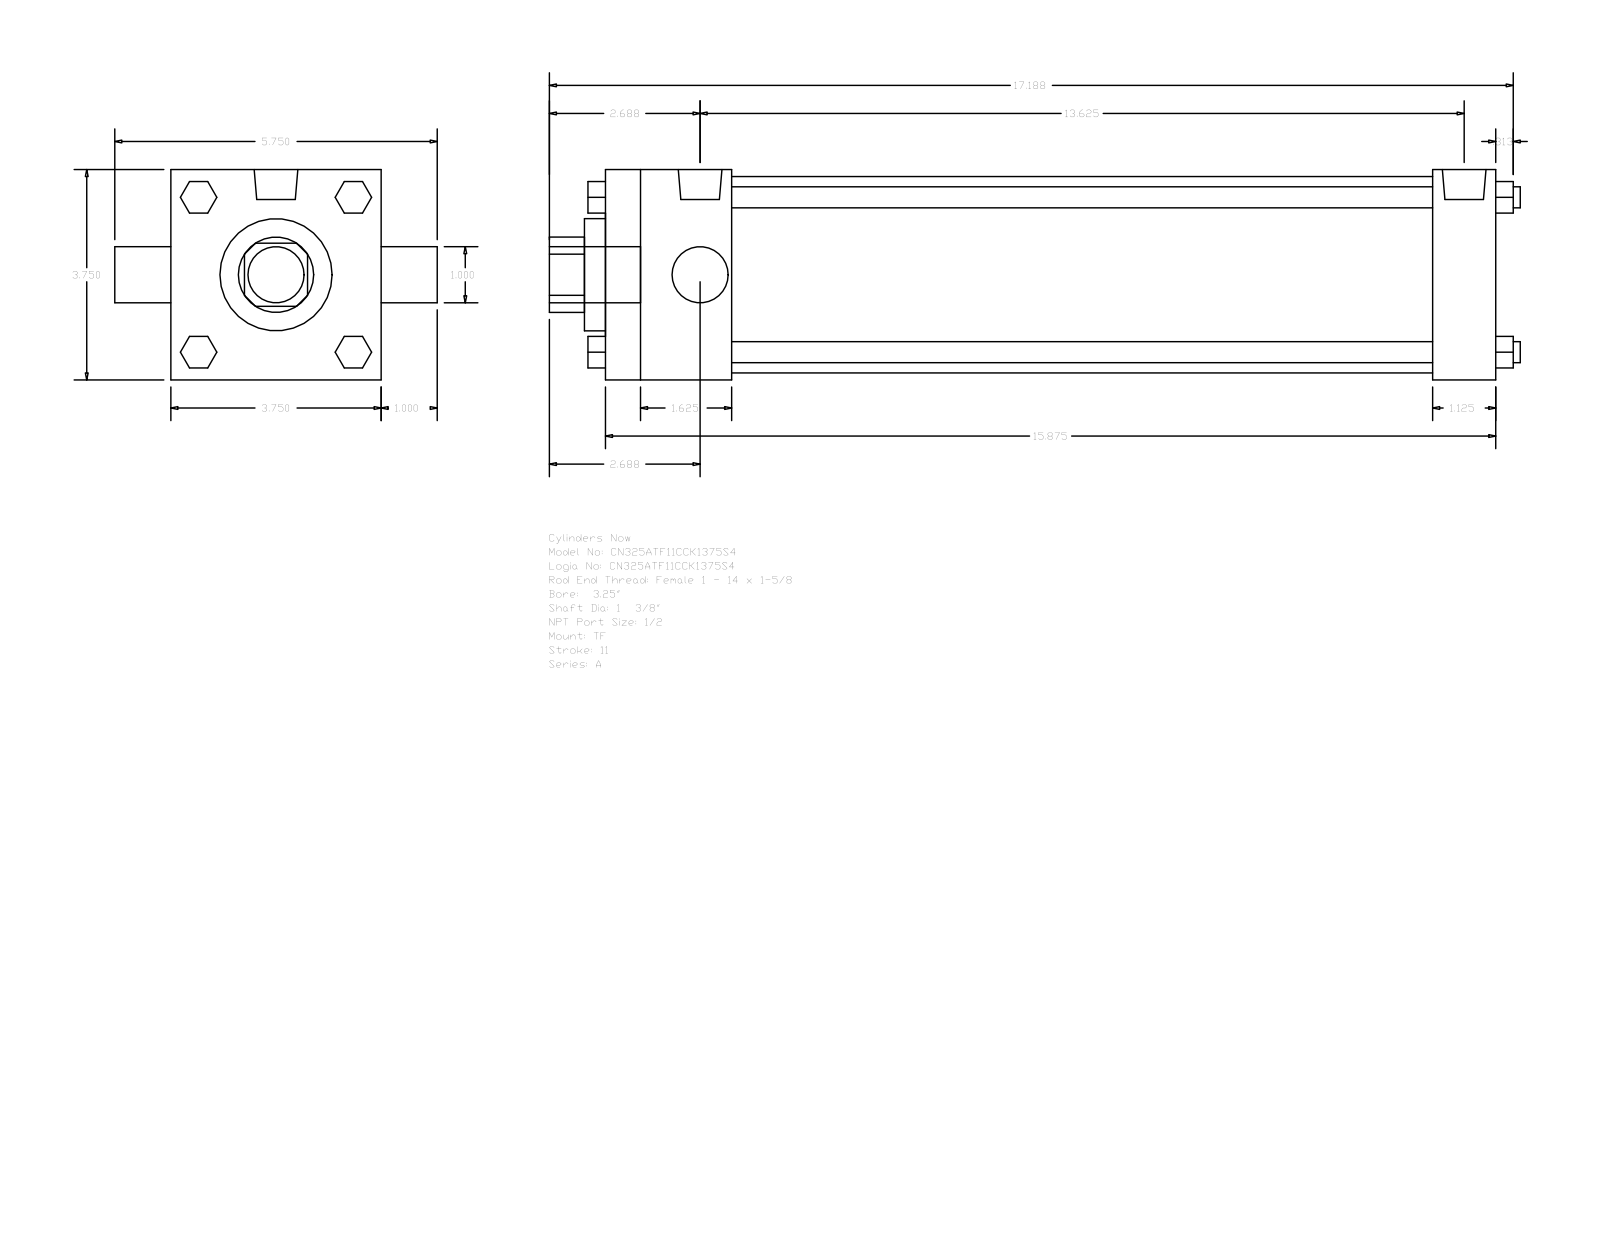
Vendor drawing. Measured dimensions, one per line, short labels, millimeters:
name: A_TF__0325_1.375
written by: GSSL Pune (CONFIG_CONTROL_DESIGN)
unit: mm
bodies: 0 solids, 120 faces (92 planar, 28 cylindrical, 0 other)
size: 439.74 × 146.05 × 95.25
holes: 1× ⌀25.4, 1× ⌀34.92, 1× ⌀50.8, 1× ⌀88.9
bosses: 4× ⌀9.53, 3× ⌀8.73, 2× ⌀19.77, 1× ⌀25.4
rounds: 1× R17.06
face distances: 95.24, 403.22, 28.57, 57.15, 374.65, 317.5, 346.07, 9.52, 66.67, 384.17
